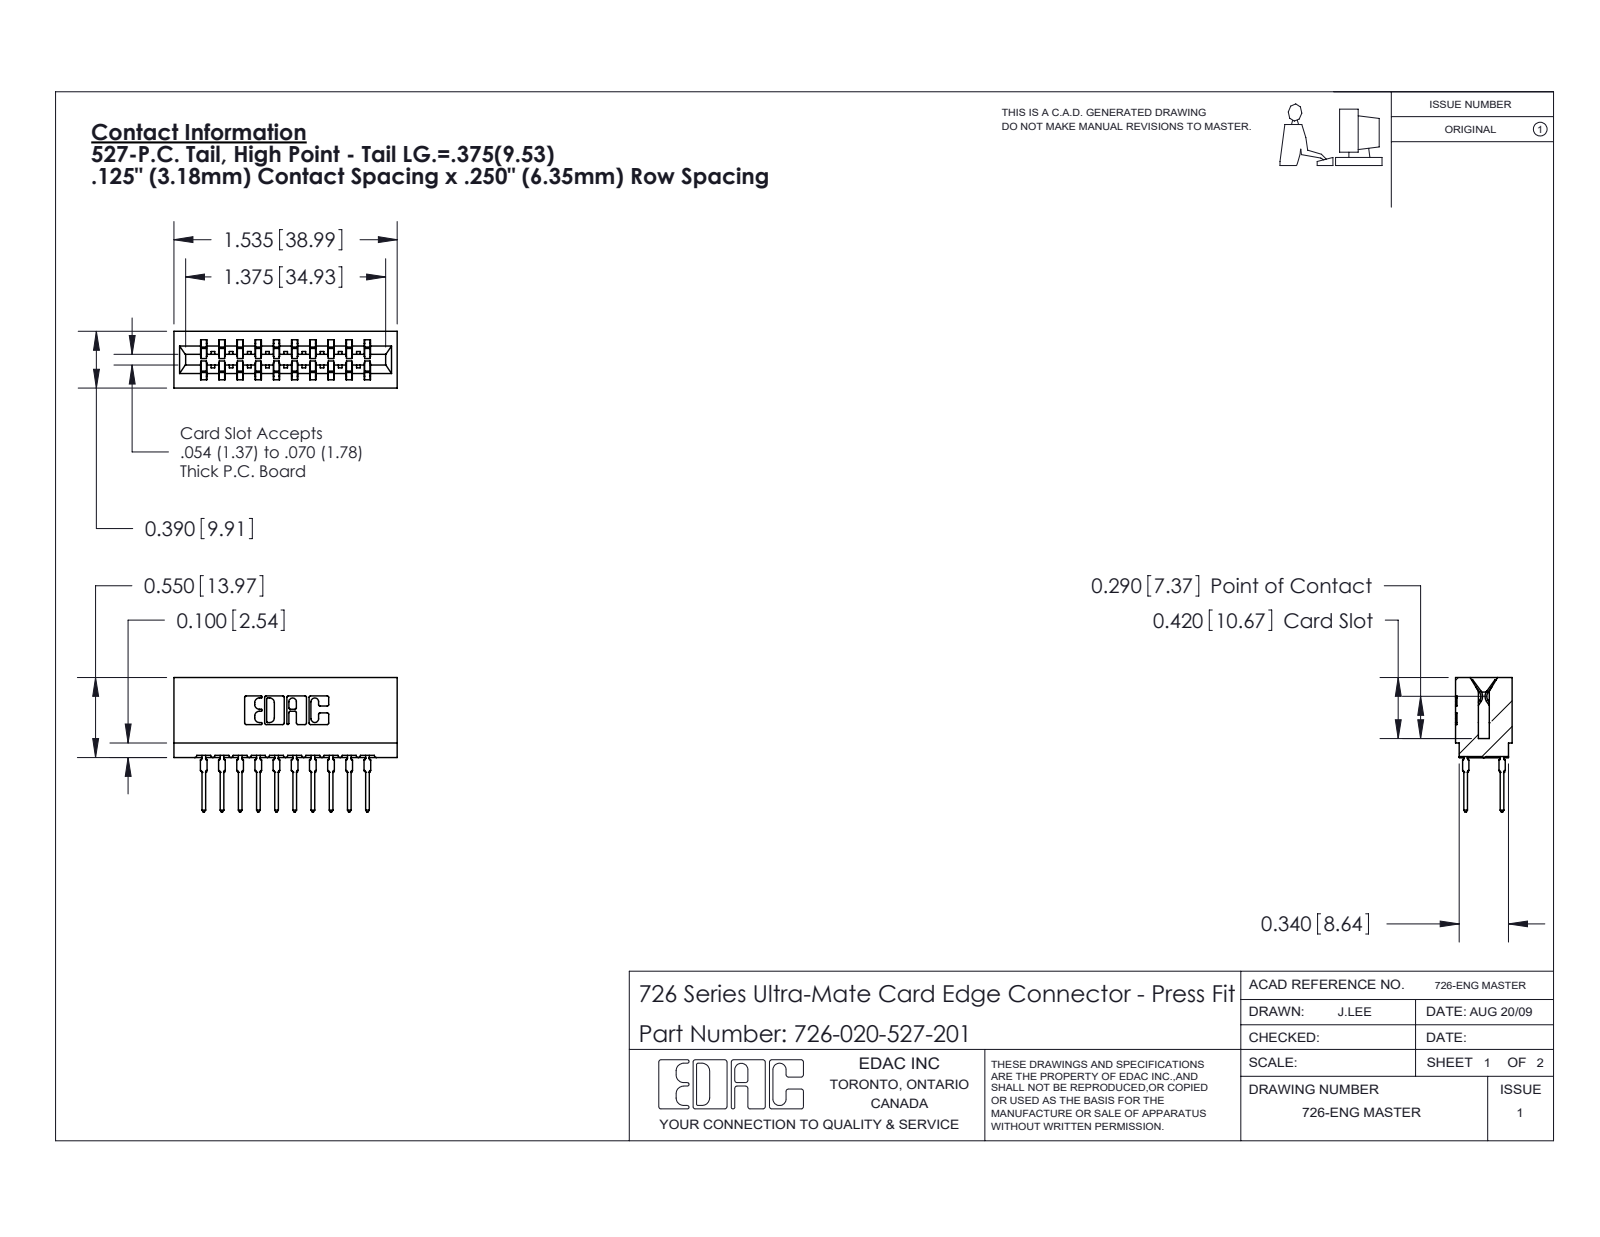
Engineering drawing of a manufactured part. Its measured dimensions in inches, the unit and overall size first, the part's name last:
Units: inches
Overall size (bounding box): 1.535 × 0.924 × 0.39
Partial cylindrical surfaces — rounded edges, fillets, slot ends (radius × count): R0.021 ×40, R0.01 ×22, R0.015 ×11, R0.005 ×8, R0.011 ×8, R0.007 ×6, R0.031 ×6, R0.026 ×3
Main face-to-face distances: 0.25, 0.057, 0.333, 0.125, 0.042, 0.75, 0.5, 0.083, 0.025, 0.307
Volume: 0.231 in³ · Surface area: 9.156 in²
Bodies: 21 solids, 1887 faces (975 planar, 392 cylindrical, 520 other)
Part name (STEP PRODUCT): 726 Part_.515 Slot Depth - 01; 726-020-527-201; 746-292-001_527
STEP written by: SolidWorks 2020 (CONFIG_CONTROL_DESIGN)
